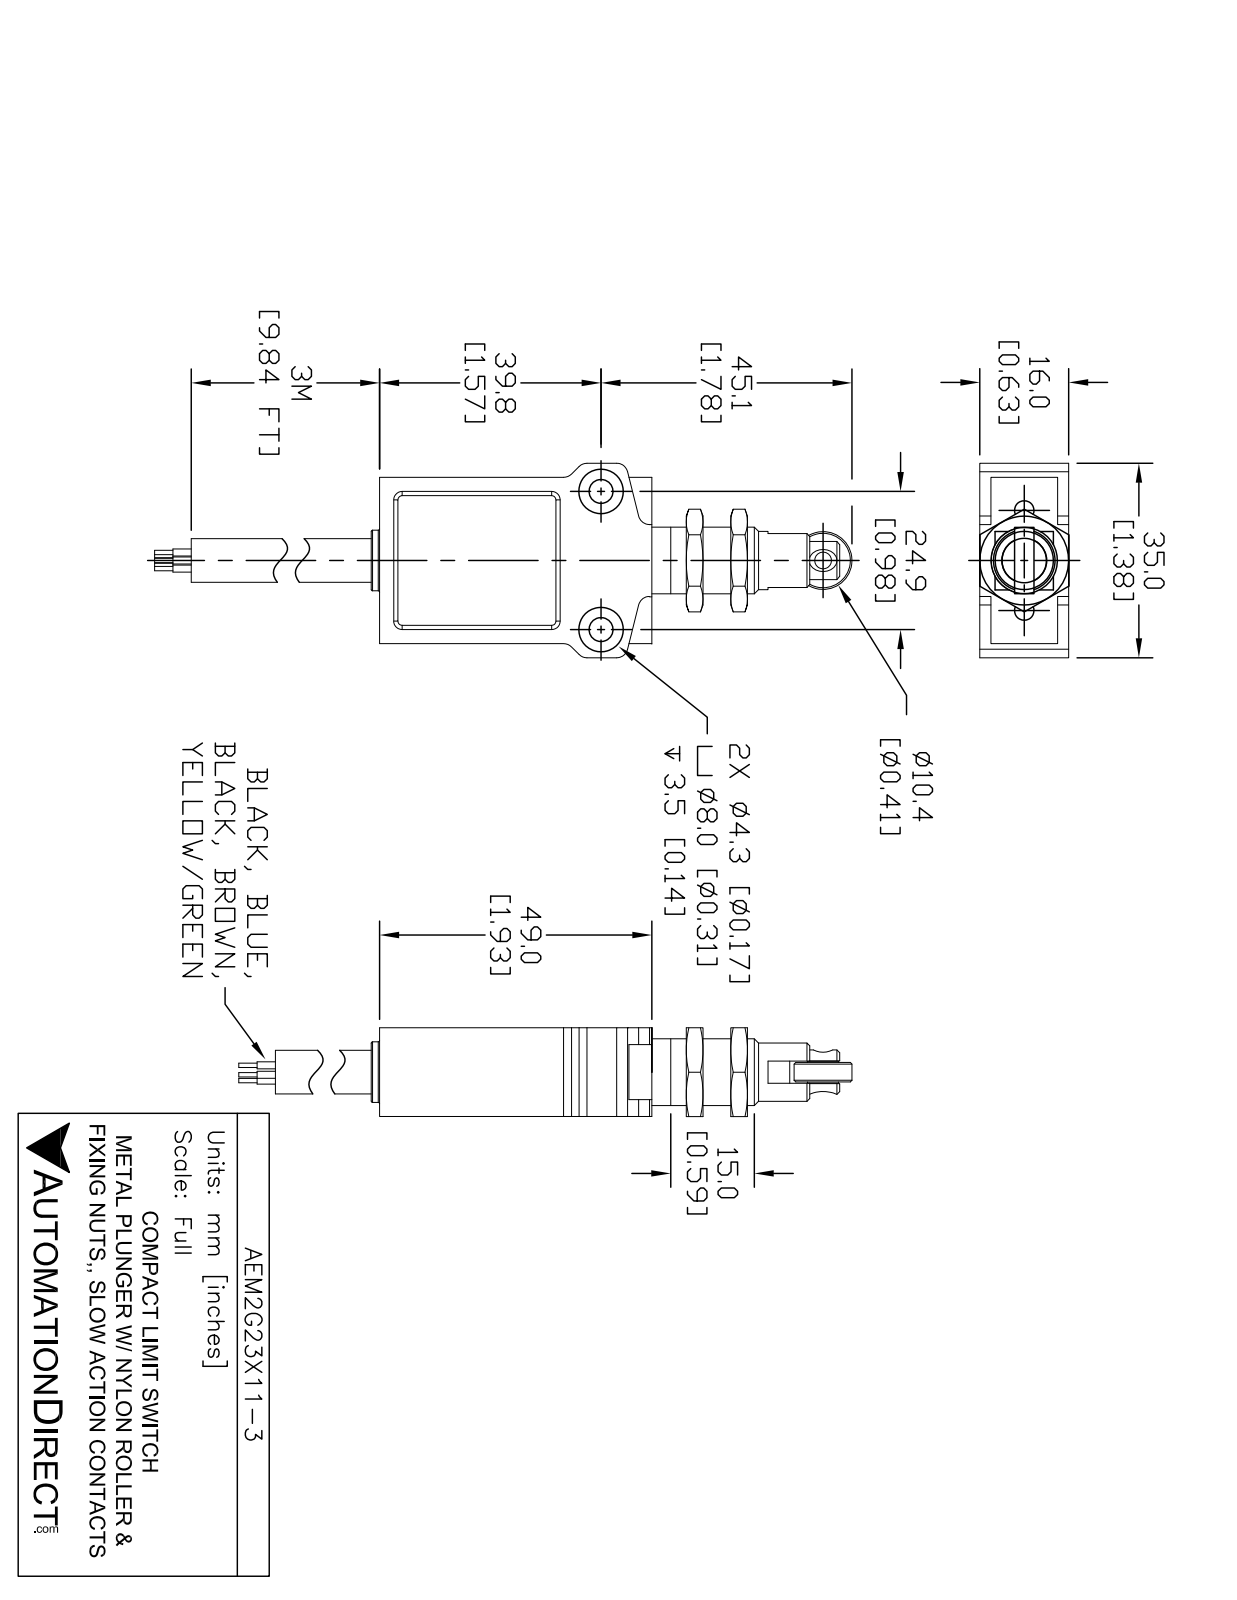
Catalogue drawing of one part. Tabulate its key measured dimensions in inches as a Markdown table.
| quantity | value |
| --- | --- |
| part name | AEM2G23X11-3_Default |
| STEP written by | SolidWorks 2021 (CONFIG_CONTROL_DESIGN) |
| units | inches |
| bodies | 2 solids, 191 faces (98 planar, 47 cylindrical, 46 other) |
| overall size | 3.965 × 1.38 × 0.63 |
| volume | 1.565 in³ |
| surface area | 14.03 in² |
| round holes (diameter × count) | 0.177 × 2, 0.344 × 2 |
| round bosses / shafts (diameter × count) | 0.05 × 5, 0.031 × 5, 0.41 × 2, 0.47 × 1, 0.43 × 1, 0.31 × 1 |
| partial cylindrical surfaces (radius × count) | 0.03 × 8, 0.08 × 8, 0.135 × 1 |
| main face-to-face distances | 0.03, 0.6, 0.57, 0.63, 1.18, 0.12, 0.3, 1.93, 0.187, 0.443 |
| hole center spacings | 0.98 |
